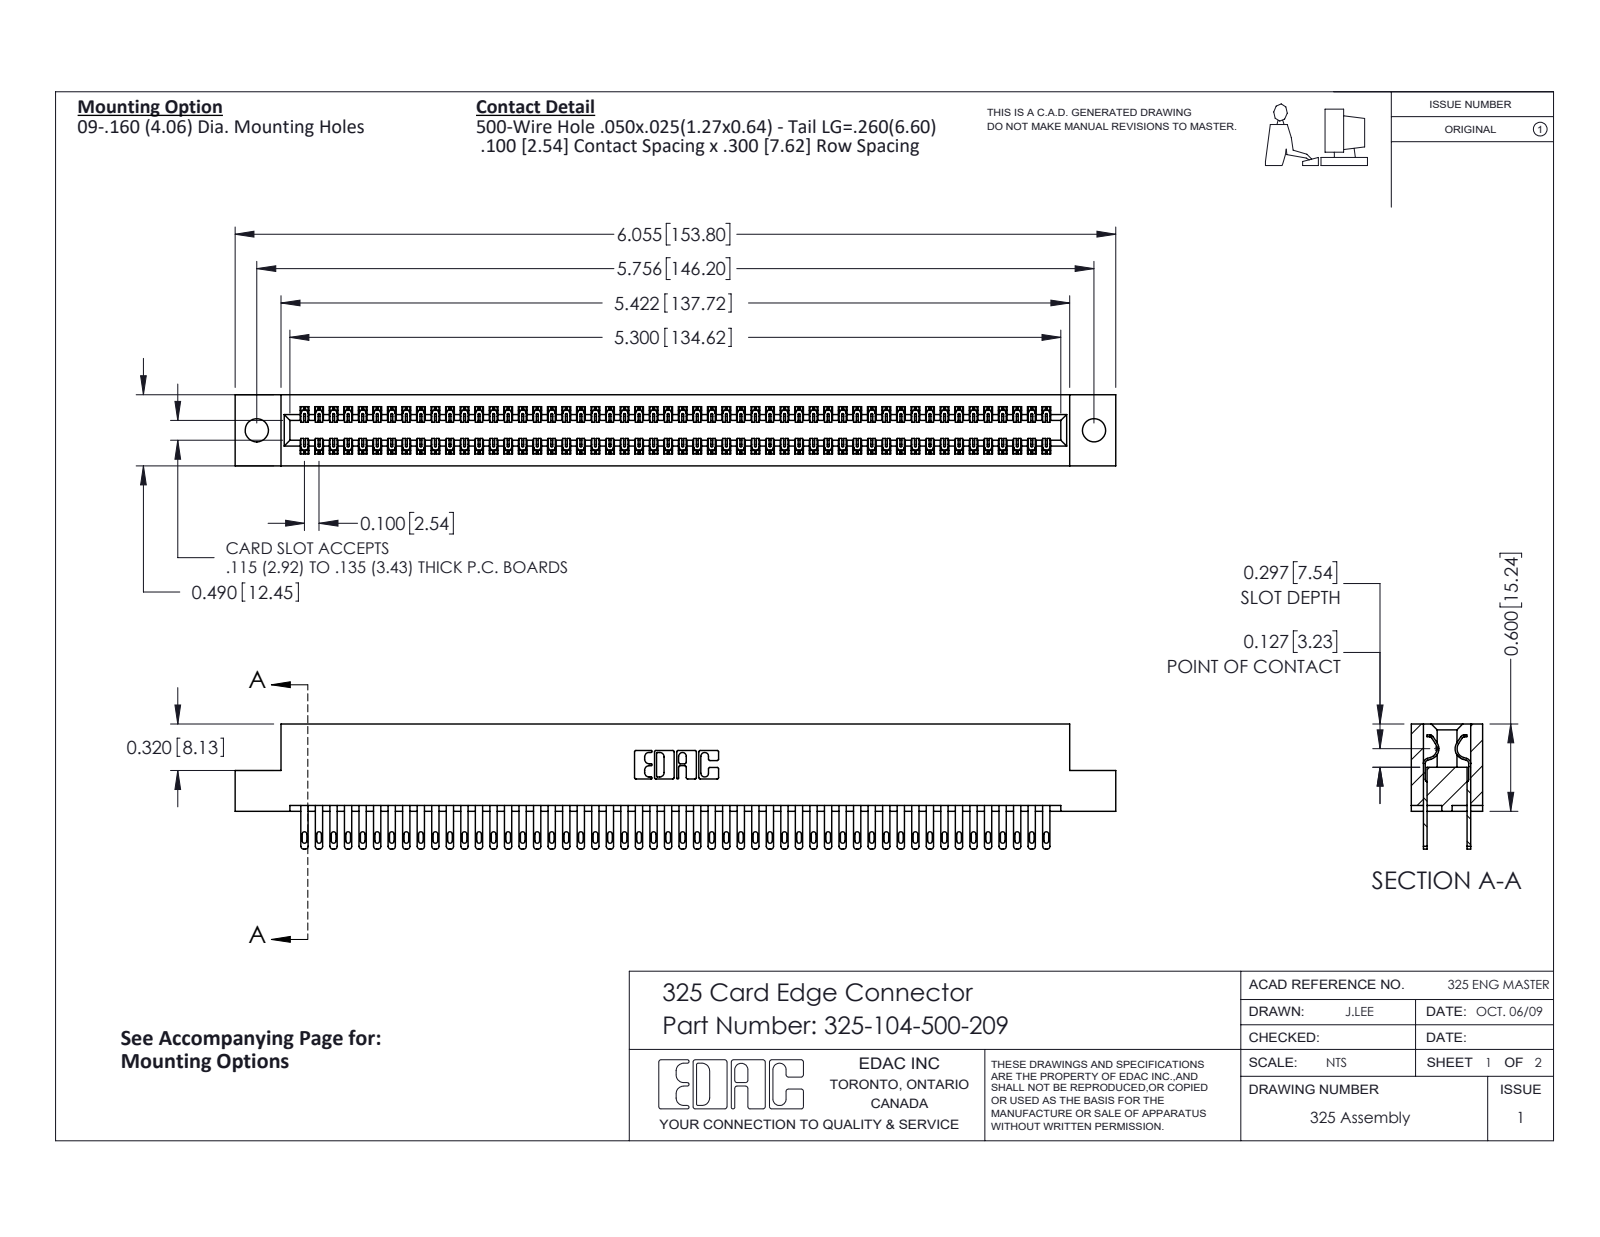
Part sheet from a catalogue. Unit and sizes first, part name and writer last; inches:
Units: inches
Overall size (bounding box): 6.055 × 0.86 × 0.49
Round holes (diameter × count): ⌀0.16 ×2
Partial cylindrical surfaces — rounded edges, fillets, slot ends (radius × count): R0.006 ×156, R0.016 ×104, R0.02 ×104, R0.01 ×22, R0.007 ×6, R0.031 ×6, R0.026 ×3, R0.014 ×2
Main face-to-face distances: 0.083, 0.407, 0.3, 0.107, 0.383, 0.025, 0.49, 0.325, 0.275, 0.56
Hole centre spacings: 5.756
Volume: 1.222 in³ · Surface area: 39.51 in²
Bodies: 105 solids, 5106 faces (3190 planar, 1916 cylindrical, 0 other)
Part name (STEP PRODUCT): 325 Part_.160 TH; 325-104-500-209; 325-292-001_325-293-100
STEP written by: SolidWorks 2016 (CONFIG_CONTROL_DESIGN)
